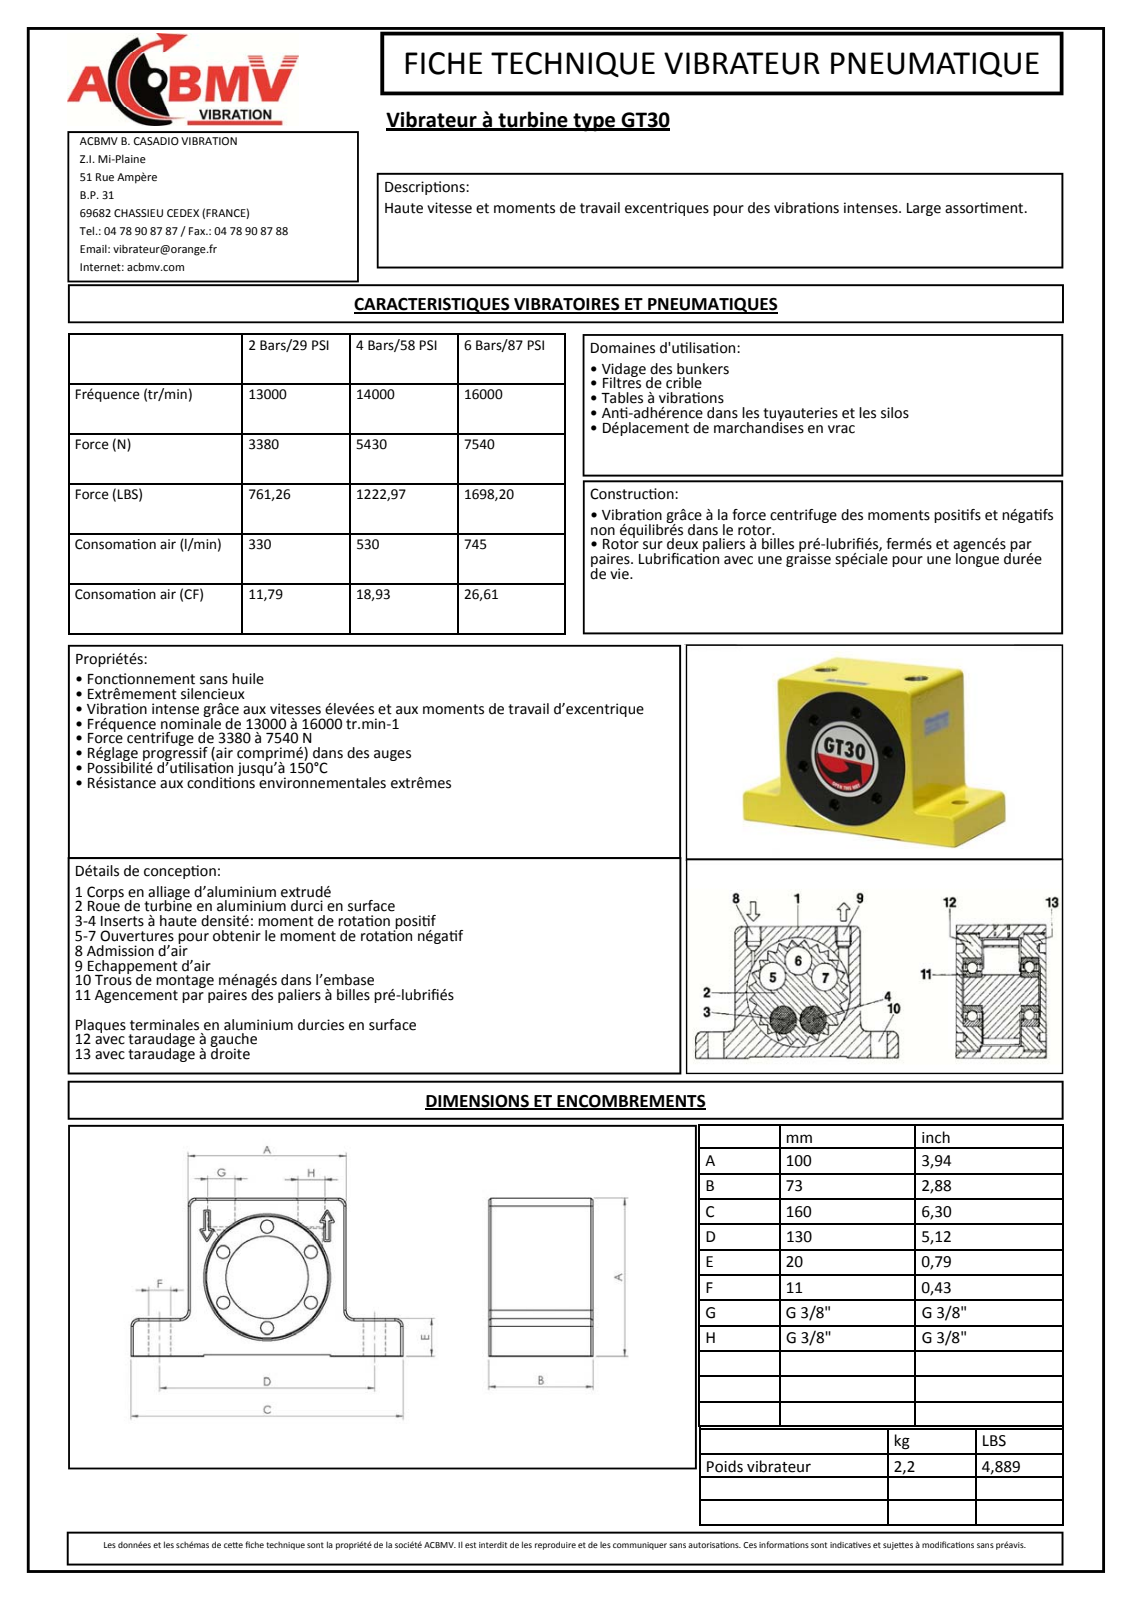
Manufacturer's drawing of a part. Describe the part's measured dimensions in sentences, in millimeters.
The part is named "8030-00-M". Its 3-D file was written by "Autodesk Inventor 2011 (CONFIG_CONTROL_DESIGN)". It is 1 solid with 275 faces: 172 planar, 73 cylindrical and 30 other. Overall it measures 160 by 100 by 73 millimeters. Its volume is 781 808 cubic millimeters and its surface area 68 469 square millimeters. Round holes: 6 of diameter 7, 4 of diameter 11, 2 of diameter 14.95, 1 of diameter 2.98, 1 of diameter 51. Round bosses or shafts: 1 of diameter 2.68. Partial cylindrical surfaces (rounded edges, fillets, slot ends): 14 of radius 0.3, 6 of radius 4, 4 of radius 0.77, 3 of radius 0.9, 3 of radius 1.03, 3 of radius 2.06, 2 of radius 0.39, 2 of radius 0.52. The main face-to-face distances are 100, 0.5, 72.7, 99.5, 73, 0.8, 72.2, 71.9, 72.4, 80. The hole center spacings are 33, 57.16, 66, 24.34, 31, 40.31, 55.17, 55.68.
